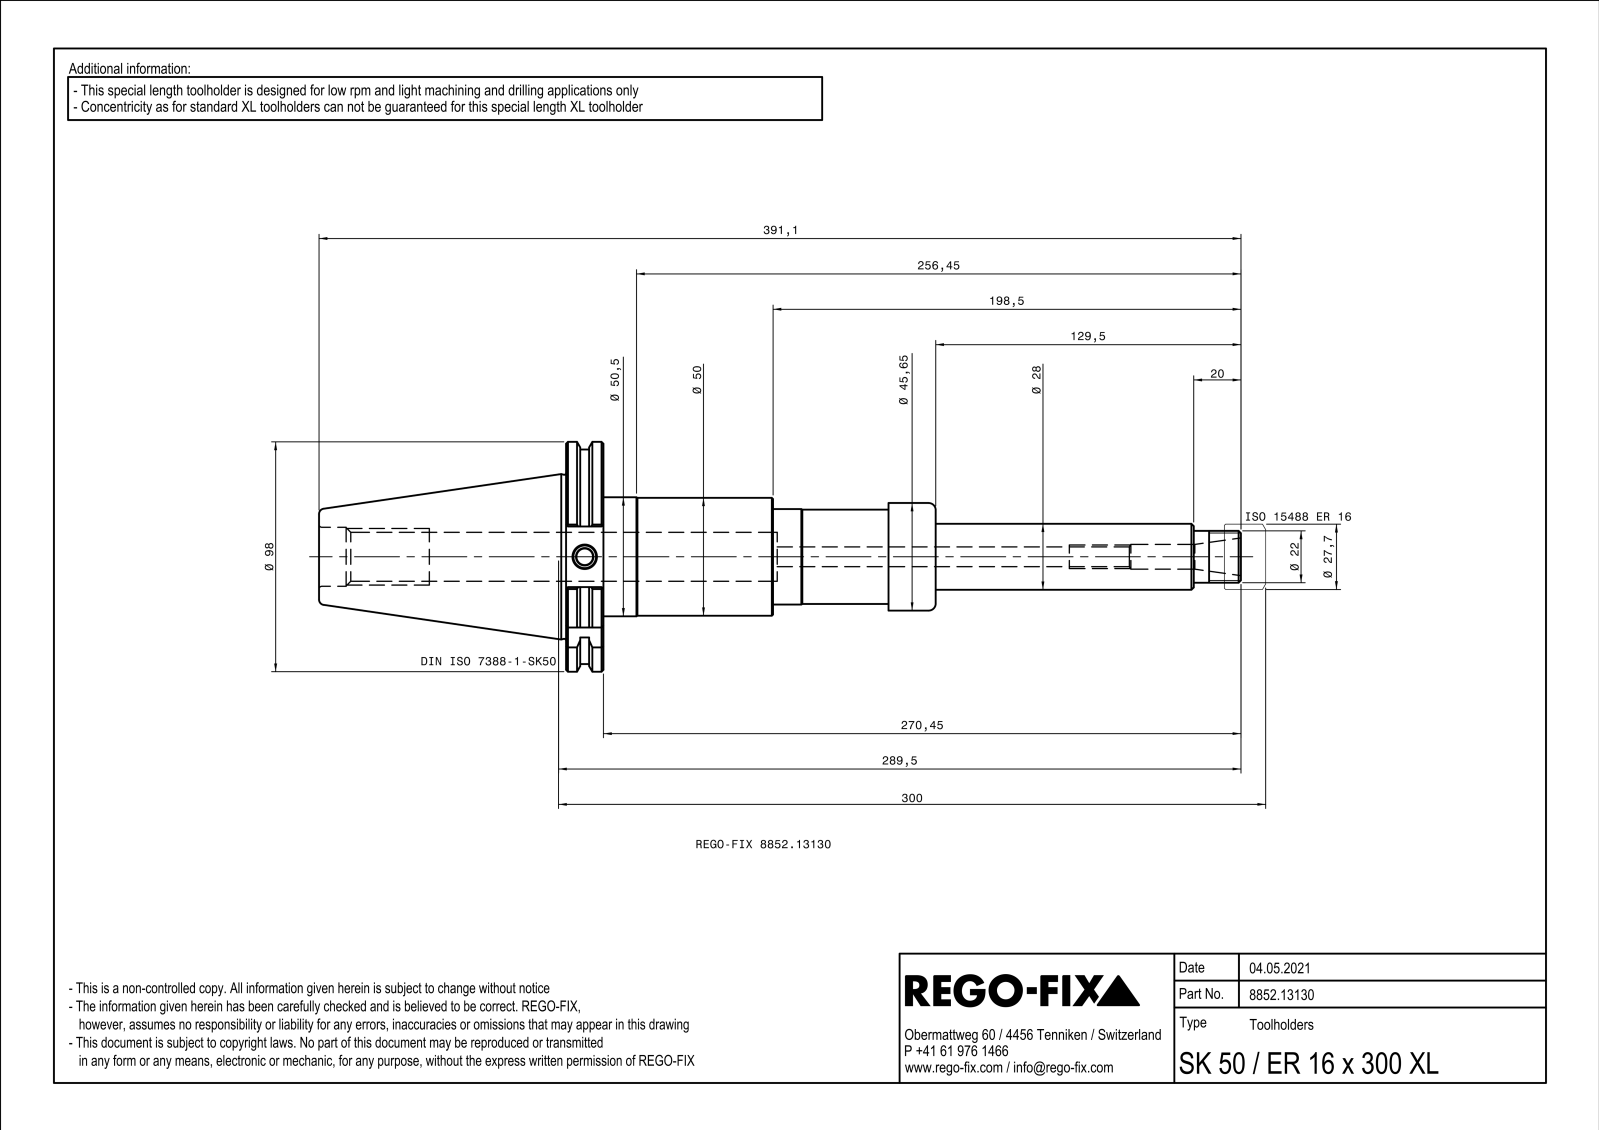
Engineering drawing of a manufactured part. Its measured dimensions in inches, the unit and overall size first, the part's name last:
Units: inches
Overall size (bounding box): 15.406 × 3.839 × 3.684
Round holes (diameter × count): ⌀0.276 ×1, ⌀0.329 ×1, ⌀0.33 ×1, ⌀0.378 ×1, ⌀0.394 ×1, ⌀0.413 ×1, ⌀0.817 ×1, ⌀0.984 ×1, ⌀1.511 ×1, ⌀1.577 ×1, ⌀1.705 ×1
Round bosses / shafts (diameter × count): ⌀3.583 ×1, ⌀1.988 ×1, ⌀1.969 ×1, ⌀1.797 ×1, ⌀1.594 ×1, ⌀1.575 ×1, ⌀1.339 ×1, ⌀1.311 ×1
Partial cylindrical surfaces — rounded edges, fillets, slot ends (radius × count): R0.02 ×5, R1.919 ×1
Main face-to-face distances: 0.624, 5.549, 6.173, 0.236, 0.551, 10.299, 4.75, 4.126, 2.717, 2.833
Volume: 35.74 in³ · Surface area: 144.2 in²
Bodies: 1 solid, 163 faces (54 planar, 38 cylindrical, 71 other)
Part name (STEP PRODUCT): NOCUT
STEP written by: SIEMENS PLM Software Solid Edge ST10 (AUTOMOTIVE_DESIGN)
